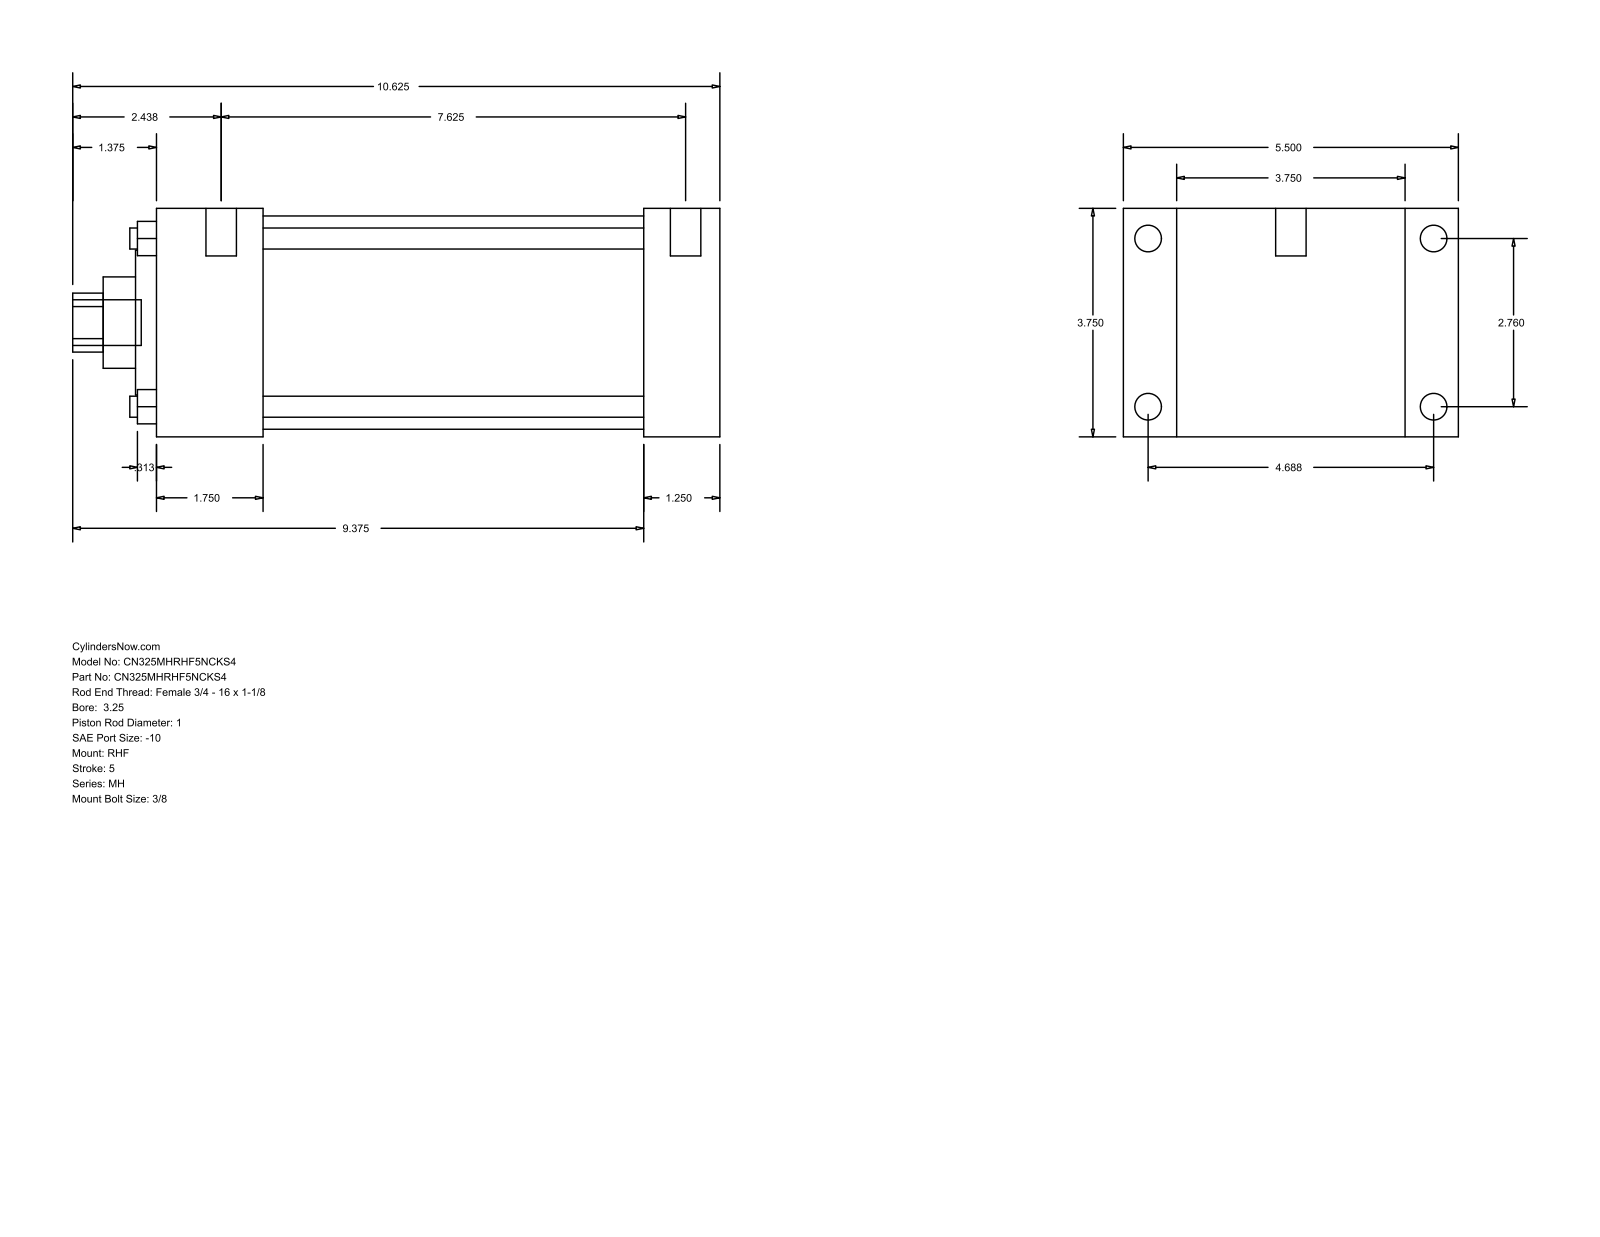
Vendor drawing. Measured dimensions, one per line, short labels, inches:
name: MH_RHF__0325_1
written by: GSSL Pune (CONFIG_CONTROL_DESIGN)
unit: in
bodies: 0 solids, 90 faces (61 planar, 29 cylindrical, 0 other)
size: 10.625 × 5.5 × 3.75
holes: 4× ⌀0.345, 1× ⌀1, 1× ⌀1.5, 1× ⌀2.375, 1× ⌀3.5
bosses: 4× ⌀0.438, 4× ⌀0.219, 2× ⌀0.5, 1× ⌀0.75
rounds: 1× R0.484
face distances: 3.75, 1.25, 0.875, 4.625, 8, 9.25, 5.5, 1.75, 6.25, 7.5
hole spacings: 1.952, 2.76, 3.903
